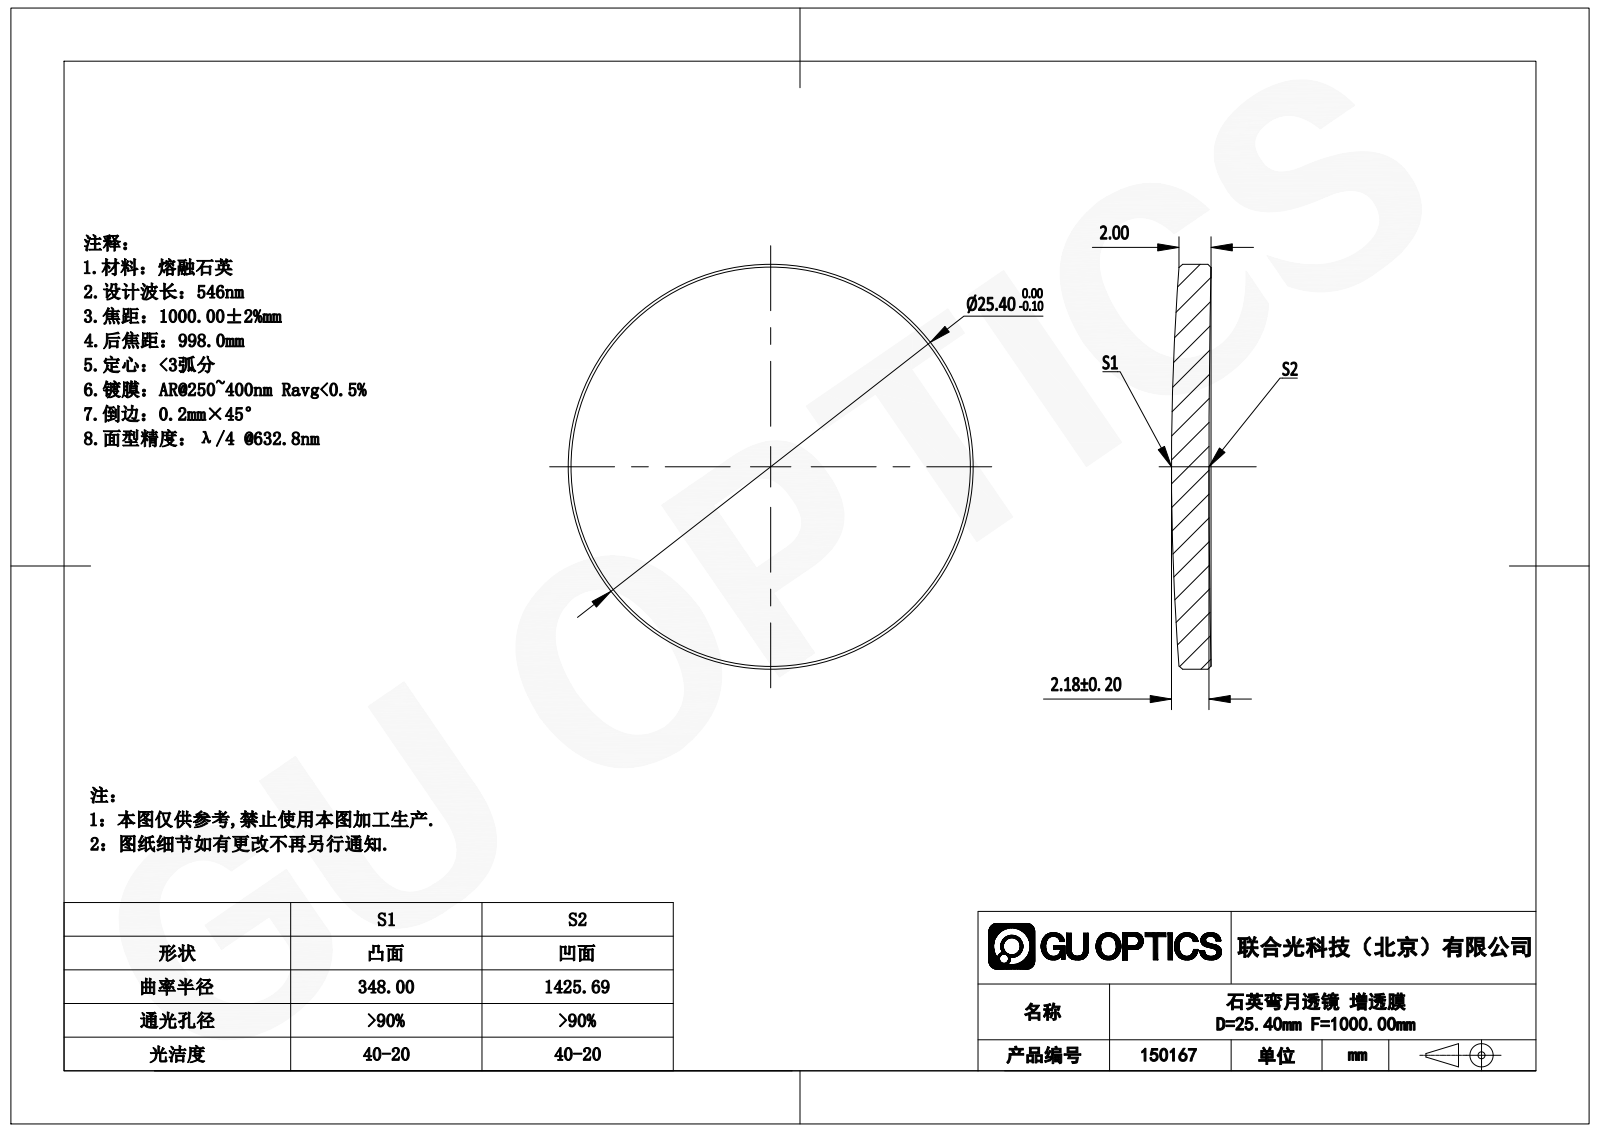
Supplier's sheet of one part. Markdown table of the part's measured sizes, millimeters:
| quantity | value |
| --- | --- |
| part name | GLM2-025B-1000-UV |
| STEP written by | SolidWorks 2022 (AUTOMOTIVE_DESIGN) |
| units | millimeters |
| bodies | 1 solid, 10 faces (0 planar, 2 cylindrical, 8 other) |
| overall size | 25.4 × 25.4 × 2.23 |
| volume | 1 055 mm³ |
| surface area | 1 155 mm² |
| round bosses / shafts (diameter × count) | 25.4 × 1 |
